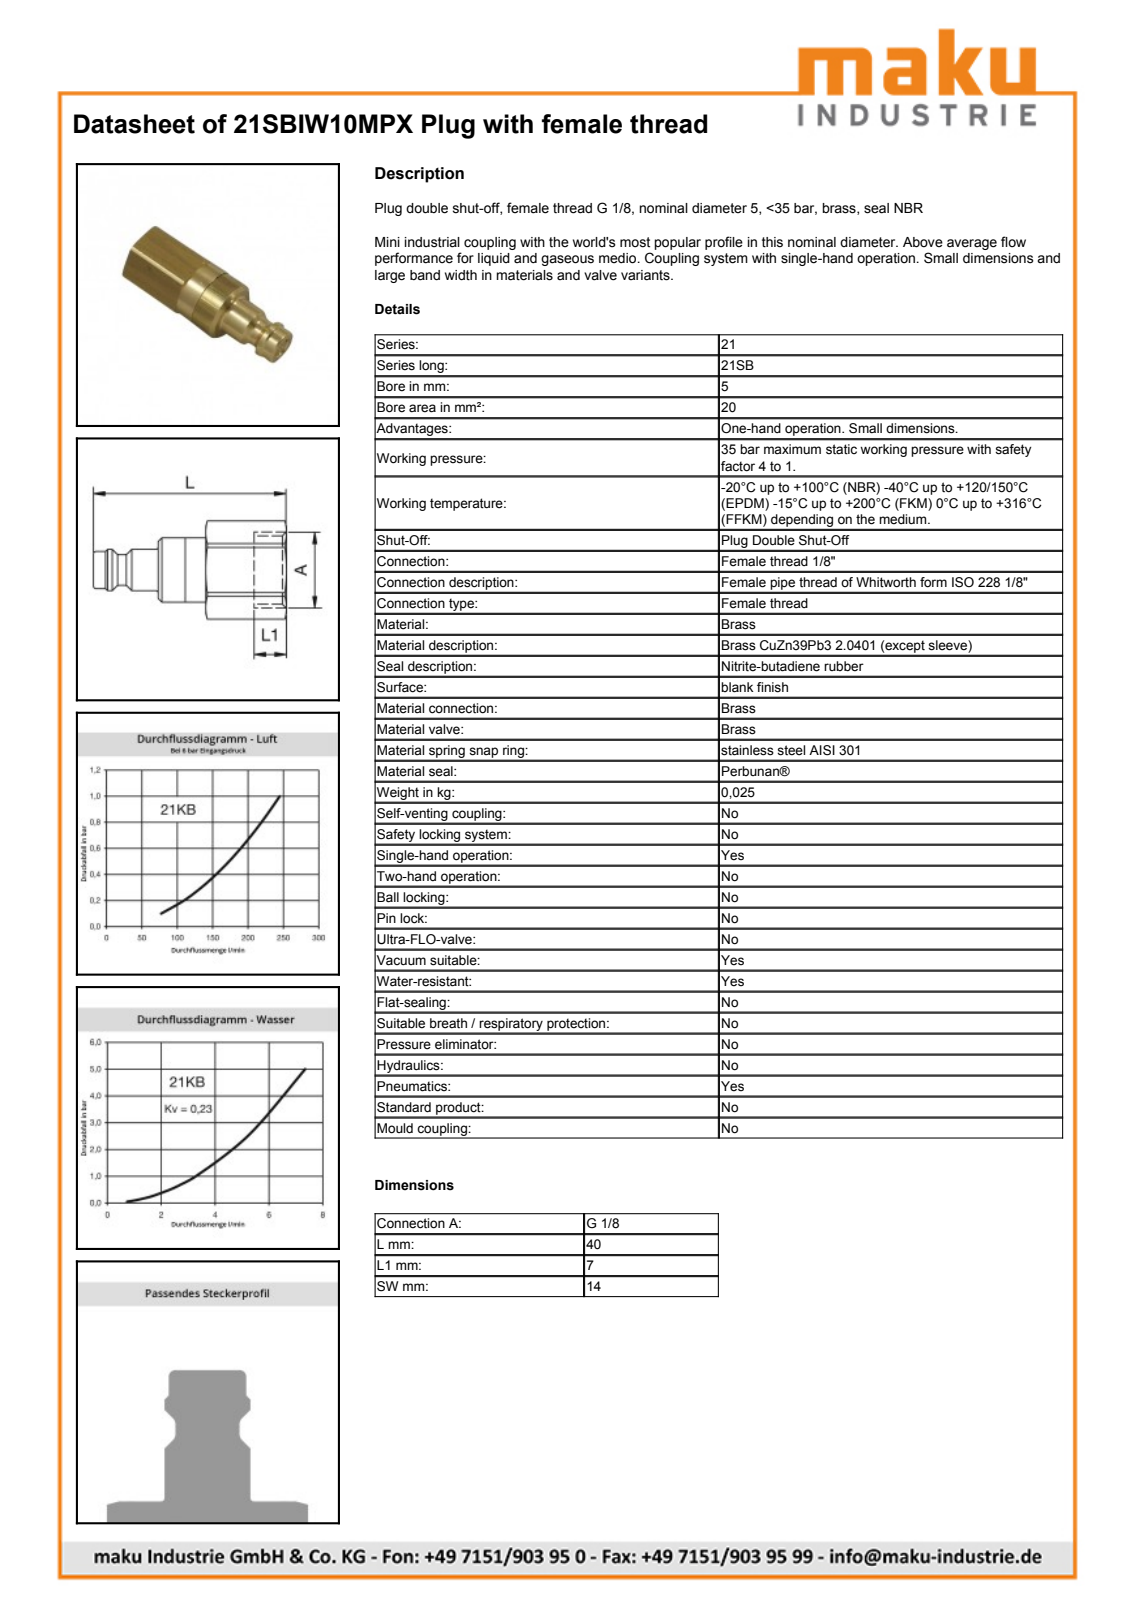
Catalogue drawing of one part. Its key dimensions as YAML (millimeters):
part_name: "D106148"
step_written_by: "Autodesk Inventor 2013 (AUTOMOTIVE_DESIGN)"
units: millimeters
bodies: {solids: 1, faces: 44, planar: 10, cylindrical: 12, other: 22}
overall_size: [40, 15.8, 14.12]
volume: 4490
surface_area: 2099
round_holes:
  - {diameter: 8.57, count: 1}
round_bosses_or_shafts:
  - {diameter: 14, count: 1}
  - {diameter: 9, count: 1}
  - {diameter: 8.1, count: 1}
  - {diameter: 6.65, count: 1}
partial_cylinders:
  - {radius: 7.9, count: 1}
face_to_face_distances: [14, 8.46, 17.44, 25.9, 14.1, 31.54, 40]
